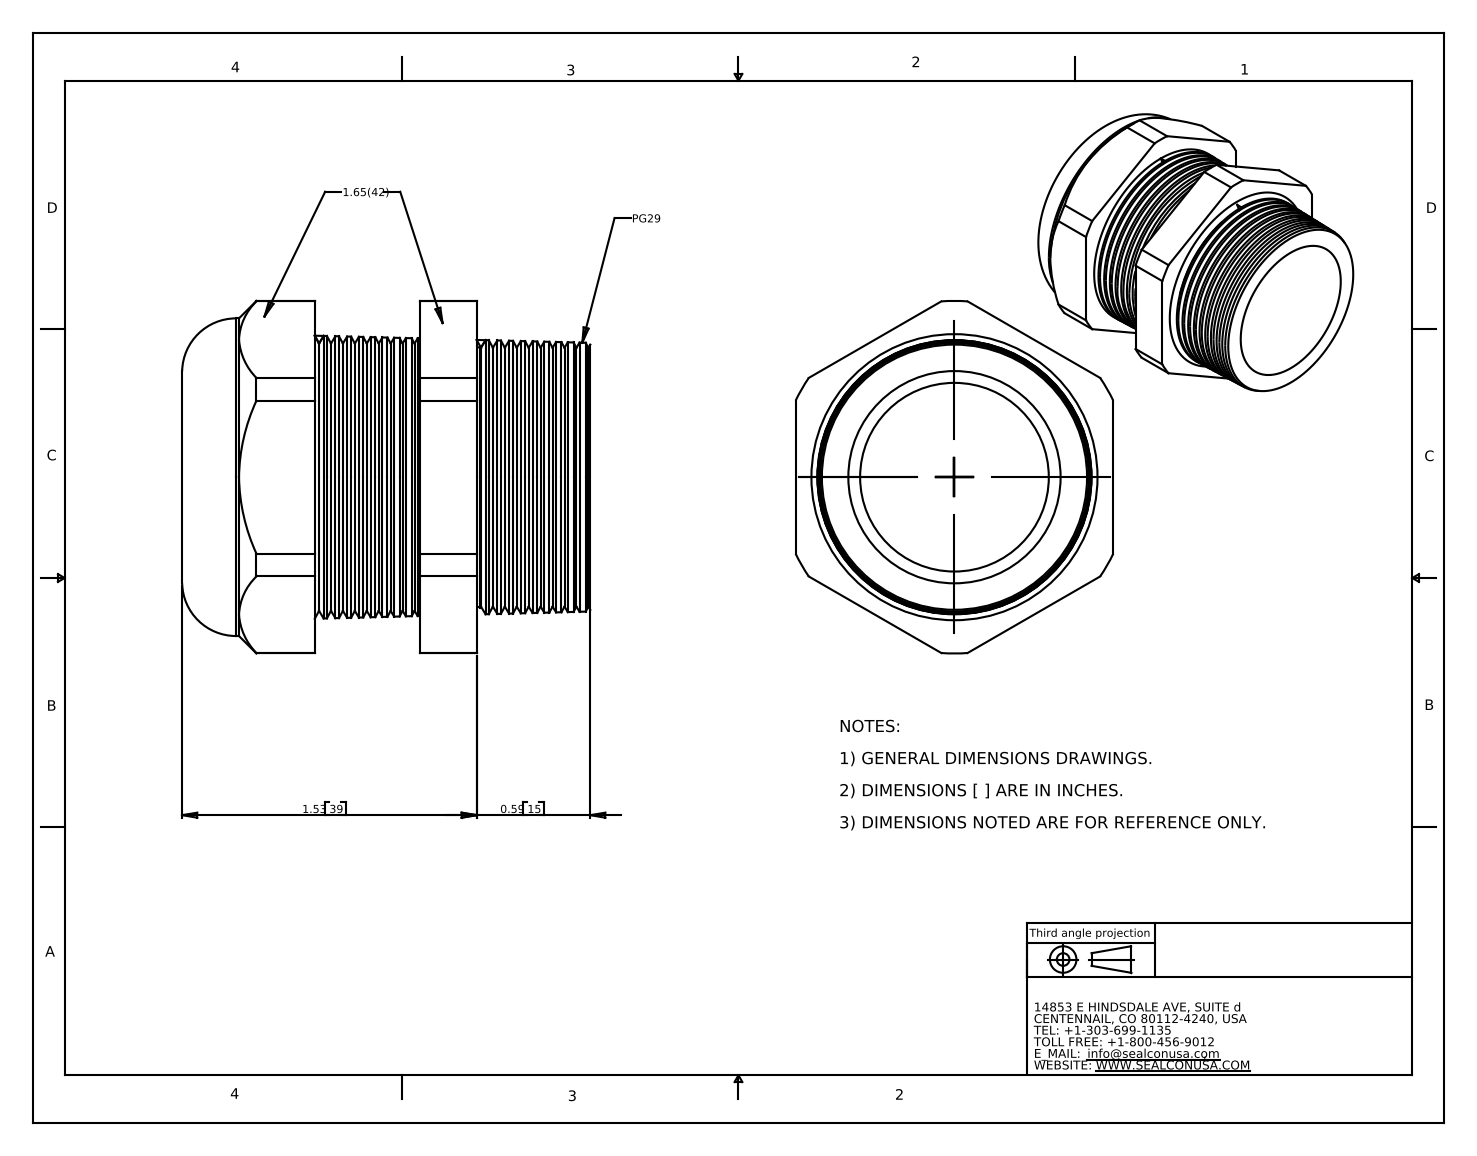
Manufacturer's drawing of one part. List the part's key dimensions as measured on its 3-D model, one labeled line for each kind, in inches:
Part name (STEP PRODUCT): CD29CA-GY
STEP written by: SolidWorks 2007 (CONFIG_CONTROL_DESIGN)
Units: inches
Bodies: 2 solids, 169 faces (19 planar, 22 cylindrical, 128 other)
Overall size (bounding box): 2.12 × 1.831 × 1.65
Volume: 2.179 in³ · Surface area: 26.32 in²
Round holes (diameter × count): ⌀0.98 ×1, ⌀1.103 ×1
Round bosses / shafts (diameter × count): ⌀1.65 ×1
Partial cylindrical surfaces — rounded edges, fillets, slot ends (radius × count): R0.916 ×1
Main face-to-face distances: 1.65, 0.546, 0.841, 0.295, 1.431, 0.885, 0.59, 1.65, 0.394, 0.94
